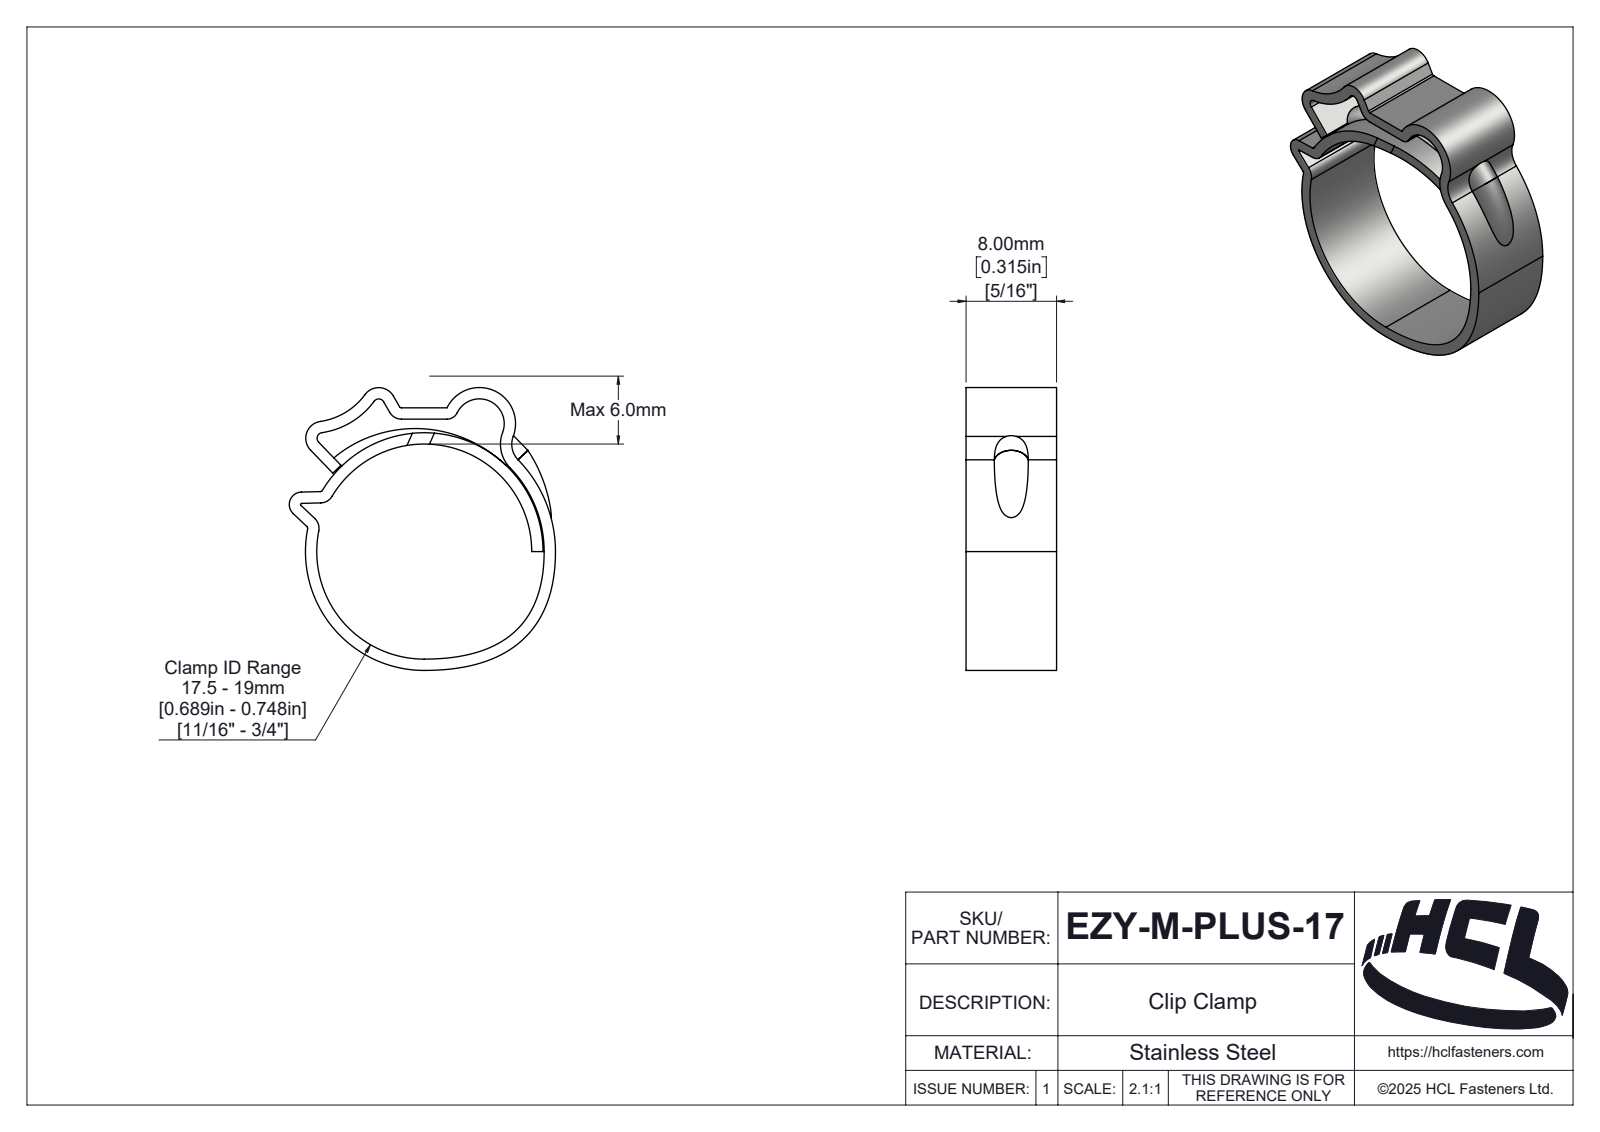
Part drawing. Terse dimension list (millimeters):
name: EZY-M-PLUS-17
written by: SolidWorks 2025 (AUTOMOTIVE_DESIGN)
unit: mm
bodies: 2 solids, 171 faces (21 planar, 86 cylindrical, 64 other)
size: 24.99 × 23.53 × 8
volume: 822 mm³; area: 1 865 mm²
rounds: 3× R0.2, 3× R1.2, 2× R0.5, 2× R1.5, 2× R10, 1× R0.1, 1× R0.23, 1× R0.94
face distances: 1, 8, 11.7, 12.7, 0.99
